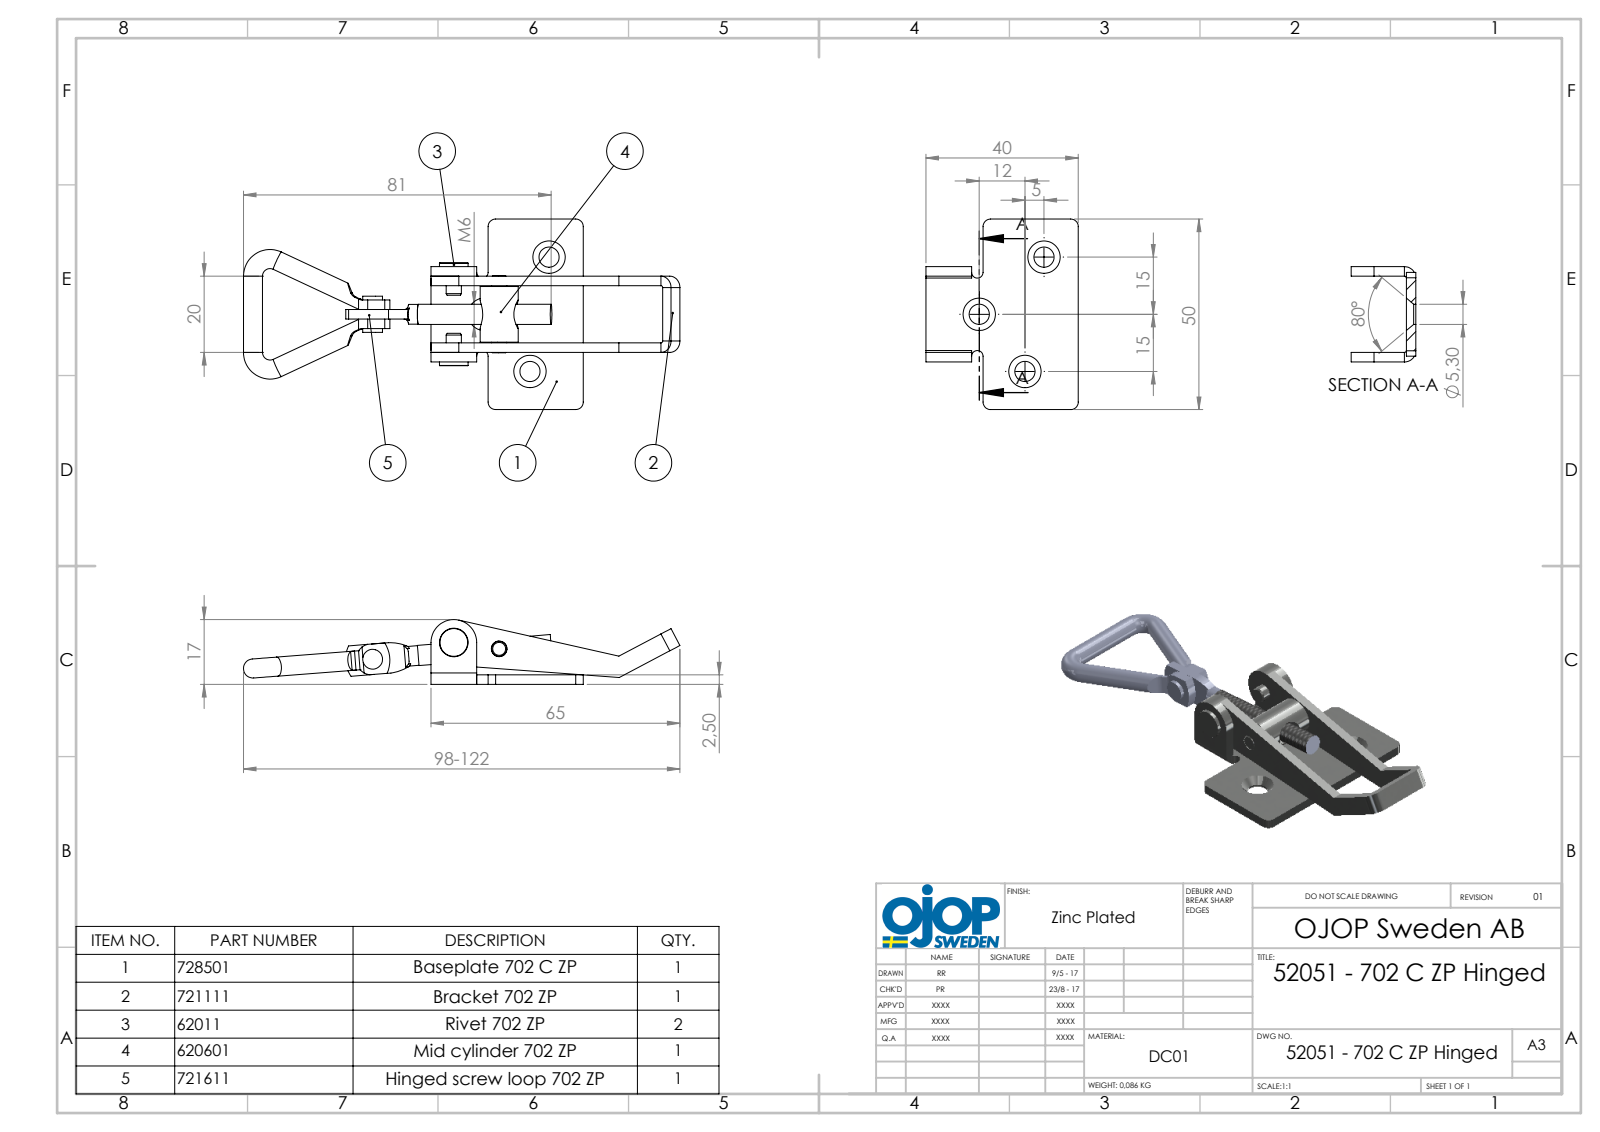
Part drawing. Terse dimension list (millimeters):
name: 702 - Rulle; 702 - Ring 702 M6; 52051 - 702 C ZP Hinged; 702 - C (+5 more)
written by: SolidWorks 2015 (AUTOMOTIVE_DESIGN)
unit: mm
bodies: 8 solids, 213 faces (82 planar, 103 cylindrical, 28 other)
size: 114.58 × 50 × 17
volume: 11 512 mm³; area: 11 486 mm²
holes: 3× ⌀4.1, 3× ⌀5.3, 1× ⌀5, 1× ⌀6
bosses: 3× ⌀5, 2× ⌀4, 1× ⌀10, 1× ⌀7.5, 1× ⌀5.3, 1× ⌀5.2, 1× ⌀5.18
rounds: 8× R2, 6× R1, 4× R0.5, 4× R3, 2× R1.5, 2× R6.78, 2× R12.31, 1× R3.85
face distances: 2.5, 17.5, 20, 8.75, 11.25, 15, 5, 6.25, 13.75, 22.5
hole spacings: 12.03, 19.21, 21.75, 22.67, 30.41, 33.32
